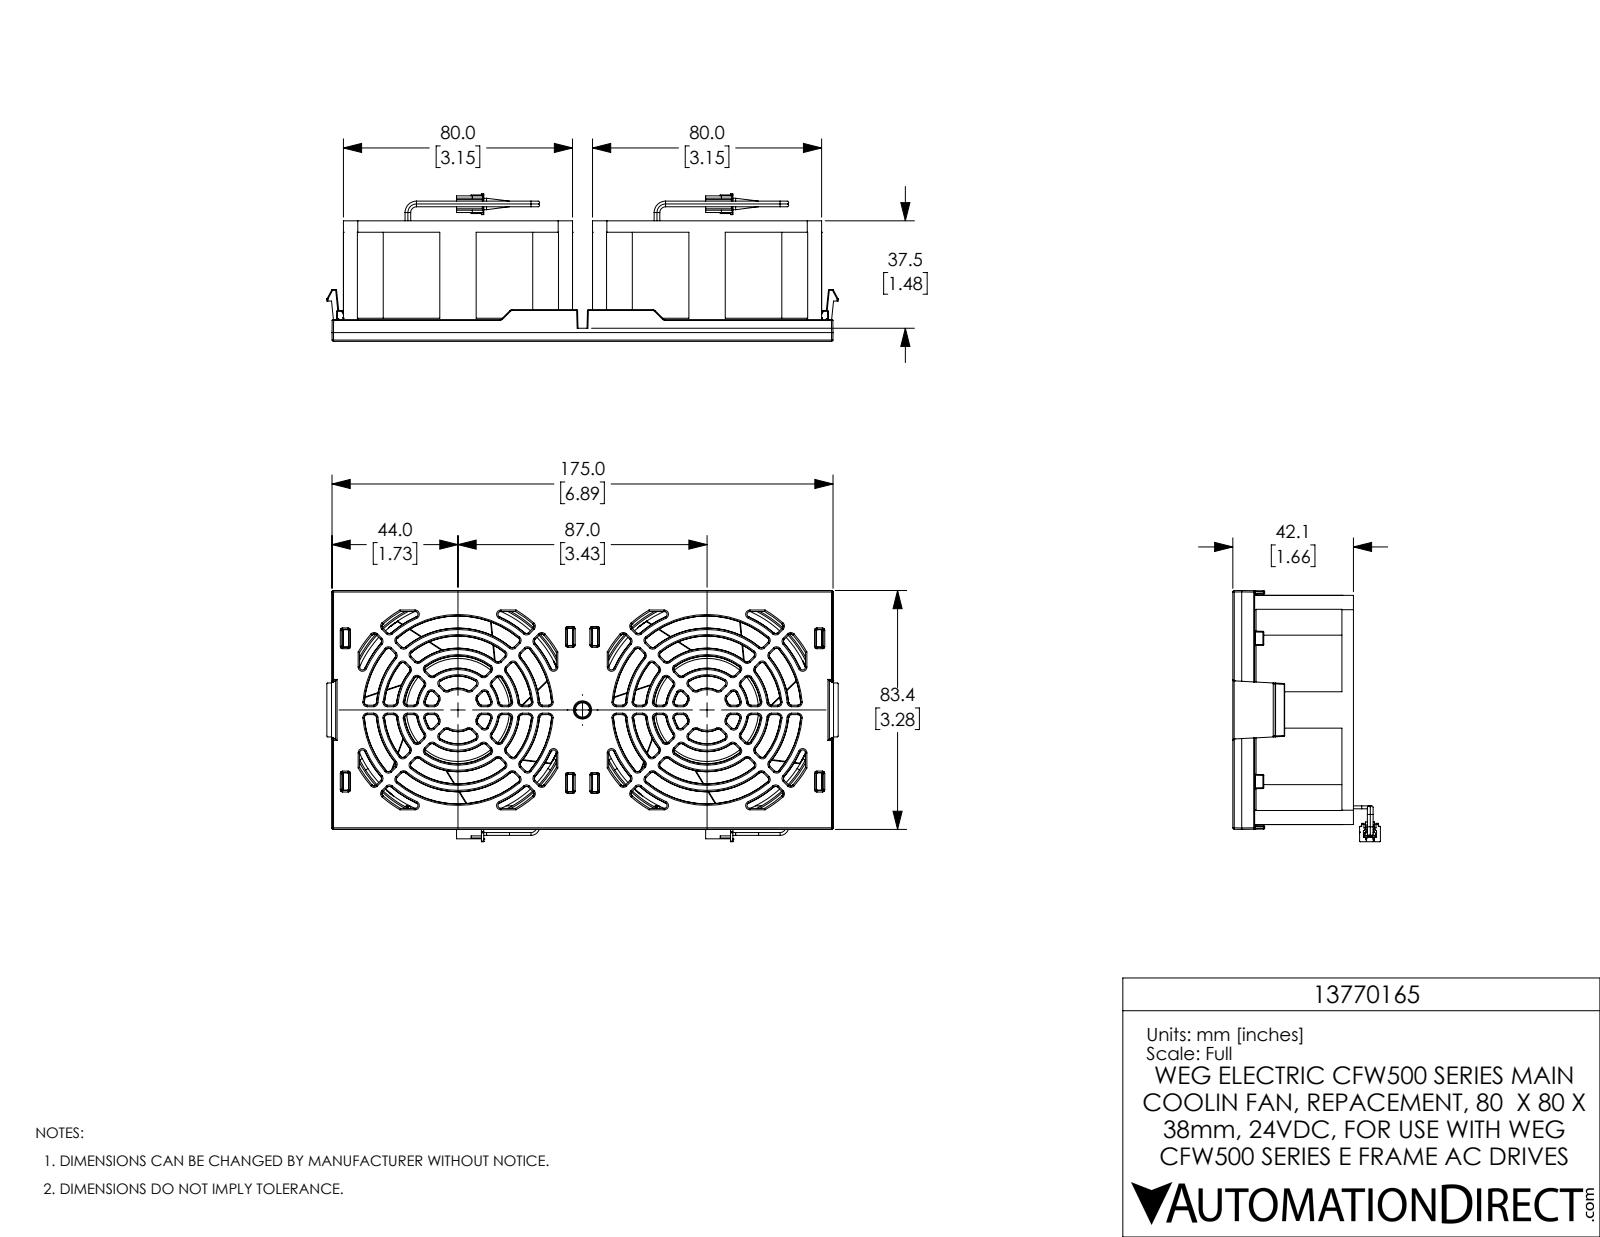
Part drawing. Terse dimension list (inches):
name: 13770165
written by: SolidWorks 2017 (AUTOMOTIVE_DESIGN)
unit: in
bodies: 9 solids, 2938 faces (961 planar, 798 cylindrical, 1179 other)
size: 7.029 × 3.453 × 2.03
volume: 12.92 in³; area: 214.2 in²
holes: 8× ⌀0.169, 2× ⌀3.031
bosses: 14× ⌀0.039, 2× ⌀2.953, 2× ⌀1.575
rounds: 270× R0.012, 48× R0.02, 16× R0.004, 8× R0.197, 4× R0.01, 4× R0.039, 2× R1.594
face distances: 0.122, 1.657, 1.535, 1.496, 0.039, 0.161, 3.15, 0.157, 1.052, 1.894
hole spacings: 1.991, 2.815, 3.425, 2.46, 3.981, 4.433, 5.033, 0.61
